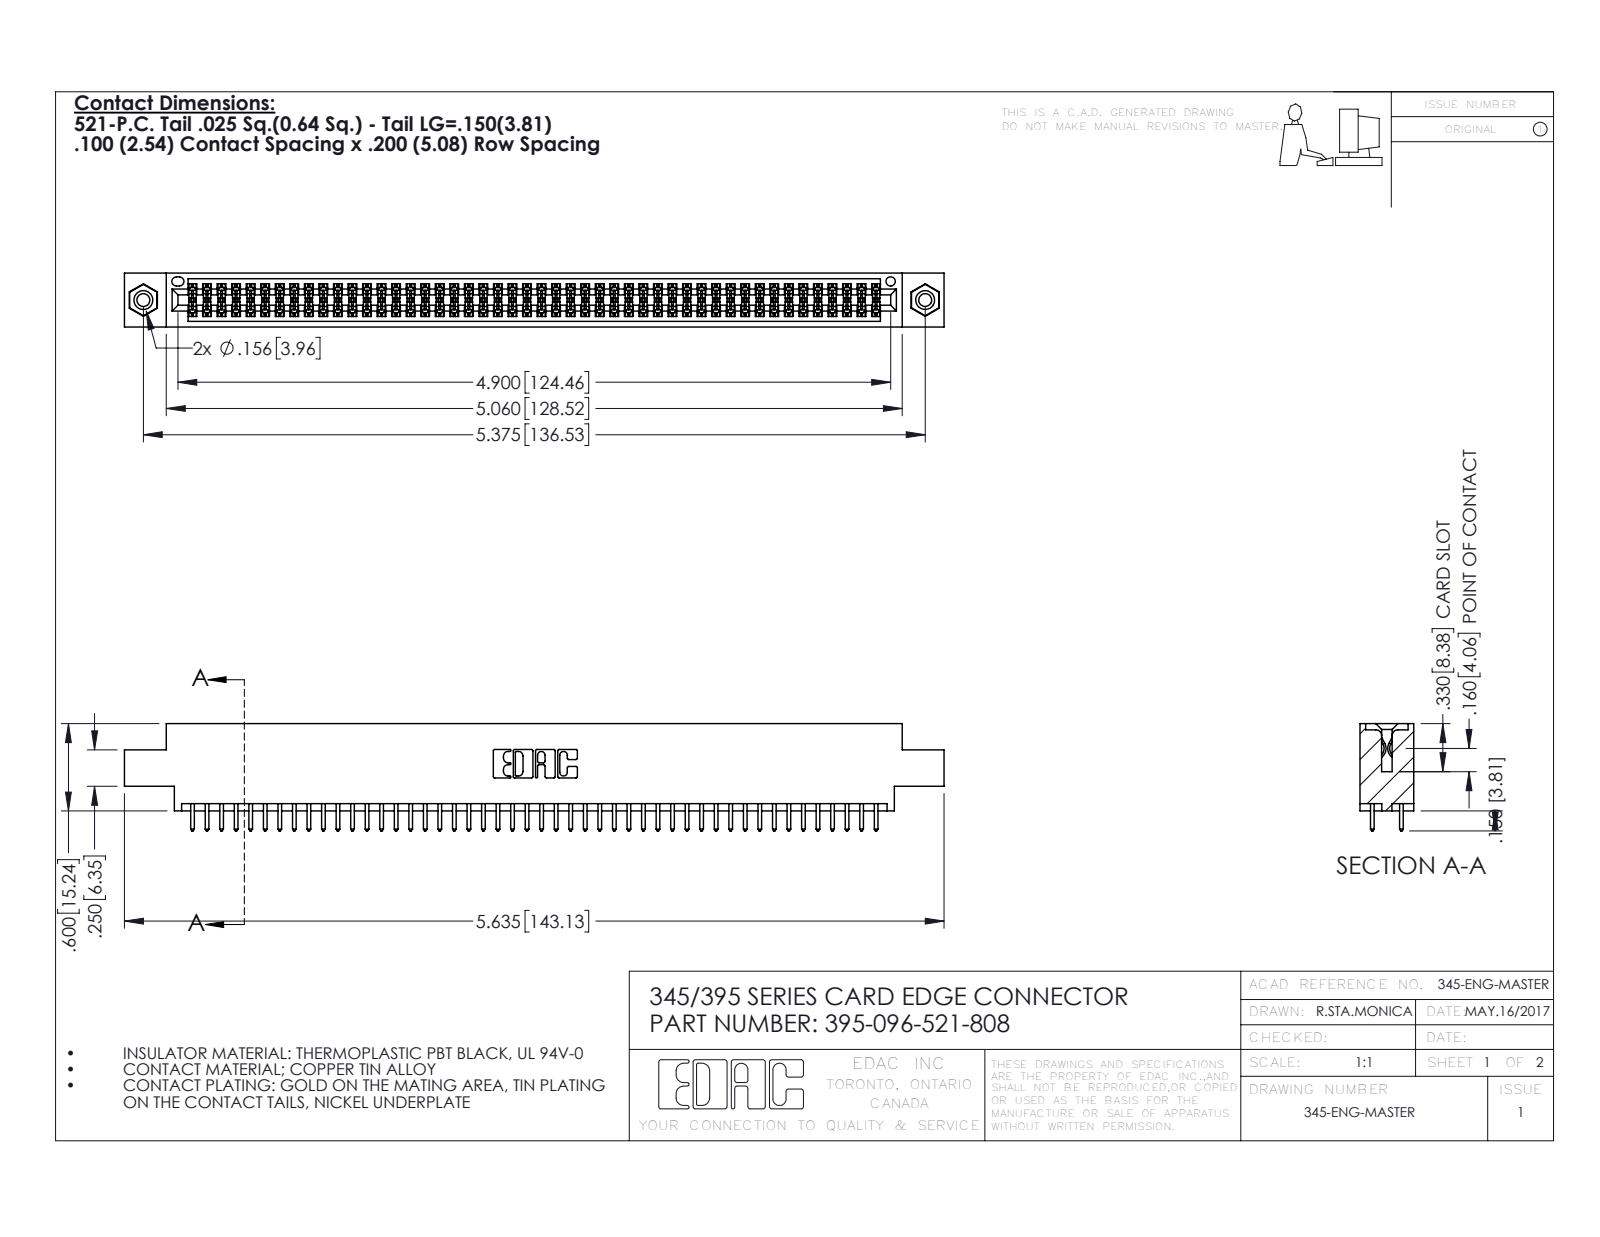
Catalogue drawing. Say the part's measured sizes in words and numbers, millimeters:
The part is named "345 Part_0.170 Offset - 0.156 Dia-TI; 345-250-001_345-250-003-102; 345-292-001_345-293-121; 395-096-521-808". Its 3-D file was written by "SolidWorks 2016 (CONFIG_CONTROL_DESIGN)". It is 99 solids with 4990 faces: 3284 planar, 1690 cylindrical and 16 other. Overall it measures 143.1 by 18.7 by 9.4 millimeters. Its volume is 13 800 cubic millimeters and its surface area 20 420 square millimeters. Round holes: 2 of diameter 2.3, 2 of diameter 3.2, 2 of diameter 4, 1 of diameter 1.6. Round bosses or shafts: 2 of diameter 3.9. Partial cylindrical surfaces (rounded edges, fillets, slot ends): 144 of radius 0.2, 96 of radius 0.3, 22 of radius 0.3, 6 of radius 0.2, 6 of radius 0.8, 3 of radius 0.7, 2 of radius 0.4, 2 of radius 0.5. The main face-to-face distances are 1.8, 7.6, 5.1, 9.4, 2.5, 6.9, 0.6, 5.7, 4.4, 3.8. The hole center spacings are 6.9, 130.5, 136.5.
